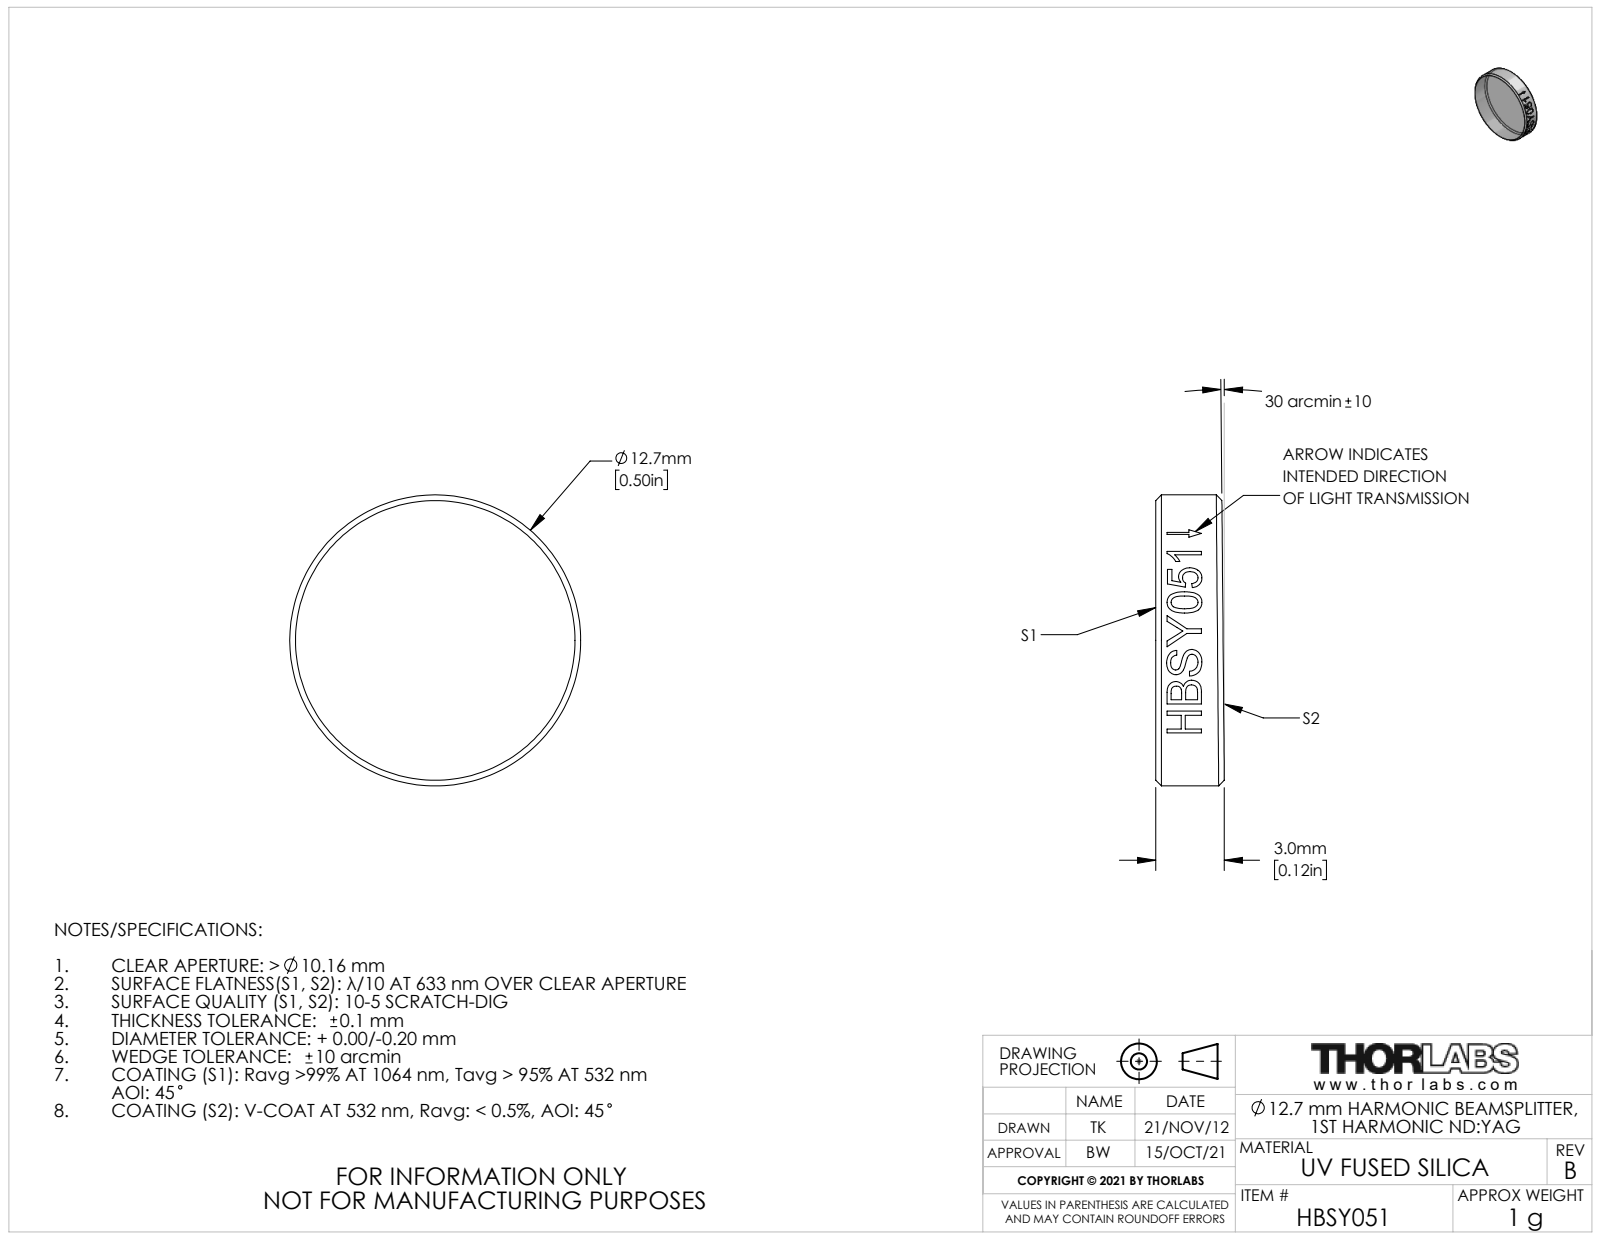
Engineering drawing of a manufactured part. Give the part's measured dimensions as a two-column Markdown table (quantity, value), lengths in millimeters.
| quantity | value |
| --- | --- |
| part name | TTN006418-E0W |
| STEP written by | SolidWorks 2012 (CONFIG_CONTROL_DESIGN) |
| units | millimeters |
| bodies | 1 solid, 19 faces (2 planar, 13 cylindrical, 4 other) |
| overall size | 12.7 × 12.7 × 3 |
| volume | 371 mm³ |
| surface area | 359 mm² |
| round bosses / shafts (diameter × count) | 12.7 × 1 |
